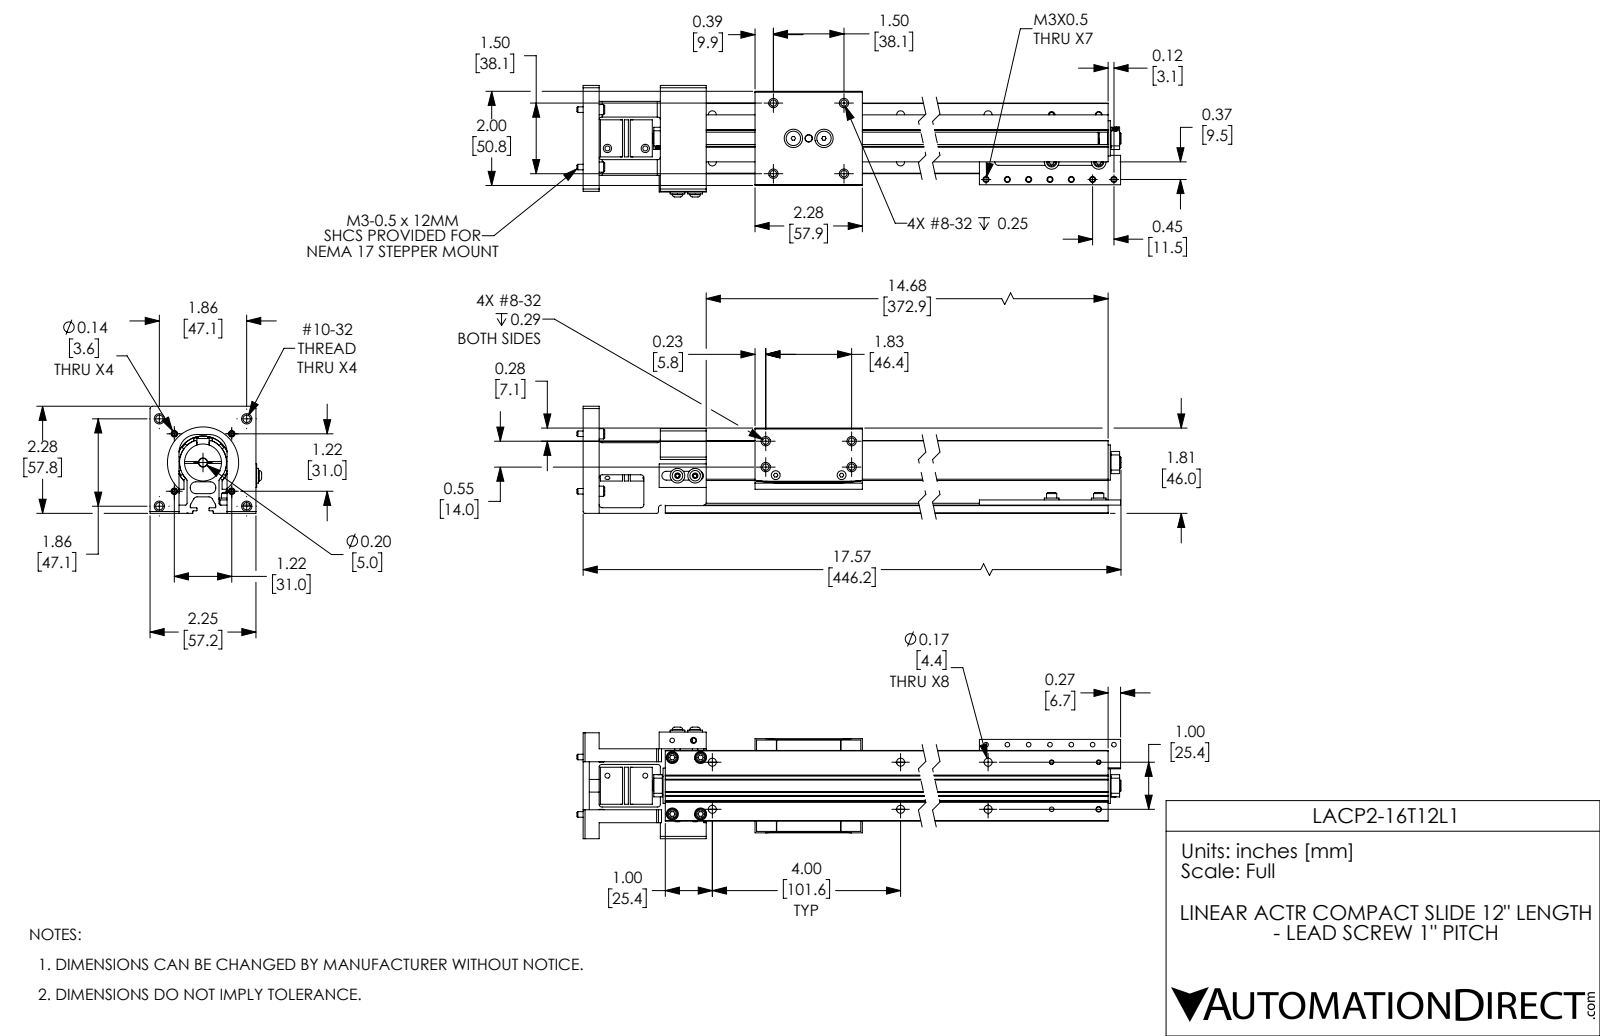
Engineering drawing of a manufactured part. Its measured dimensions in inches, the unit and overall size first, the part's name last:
Units: inches
Overall size (bounding box): 17.7 × 2.37 × 2.275
Round holes (diameter × count): ⌀0.098 ×18, ⌀0.136 ×10, ⌀0.172 ×8, ⌀0.141 ×4, ⌀0.147 ×4, ⌀0.159 ×4, ⌀0.257 ×4, ⌀0.099 ×2, ⌀0.106 ×2, ⌀0.118 ×2, ⌀0.125 ×2, ⌀0.125 ×2
Round bosses / shafts (diameter × count): ⌀0.217 ×10, ⌀0.118 ×10, ⌀0.312 ×4, ⌀0.118 ×3, ⌀0.307 ×2, ⌀0.224 ×2, ⌀0.164 ×2, ⌀0.138 ×2
Partial cylindrical surfaces — rounded edges, fillets, slot ends (radius × count): R0.01 ×17, R0.05 ×9, R0.039 ×8, R0.065 ×7, R0.02 ×4, R0.074 ×4, R0.079 ×4, R0.118 ×4
Main face-to-face distances: 0.175, 0.679, 0.34, 0.175, 1.535, 0.17, 0.849, 0.24, 0.411, 1.089
Hole centre spacings: 1, 1.2, 0.453, 0.863, 0.906, 1.128, 1.312, 1.57
Volume: 19.33 in³ · Surface area: 292.5 in²
Bodies: 46 solids, 1240 faces (502 planar, 469 cylindrical, 269 other)
Part name (STEP PRODUCT): LACP2-16T12L1; LACP2-16T12L1_BLOCK; LACP2-16T12L1_BODY
STEP written by: SolidWorks 2017 (AUTOMOTIVE_DESIGN)
